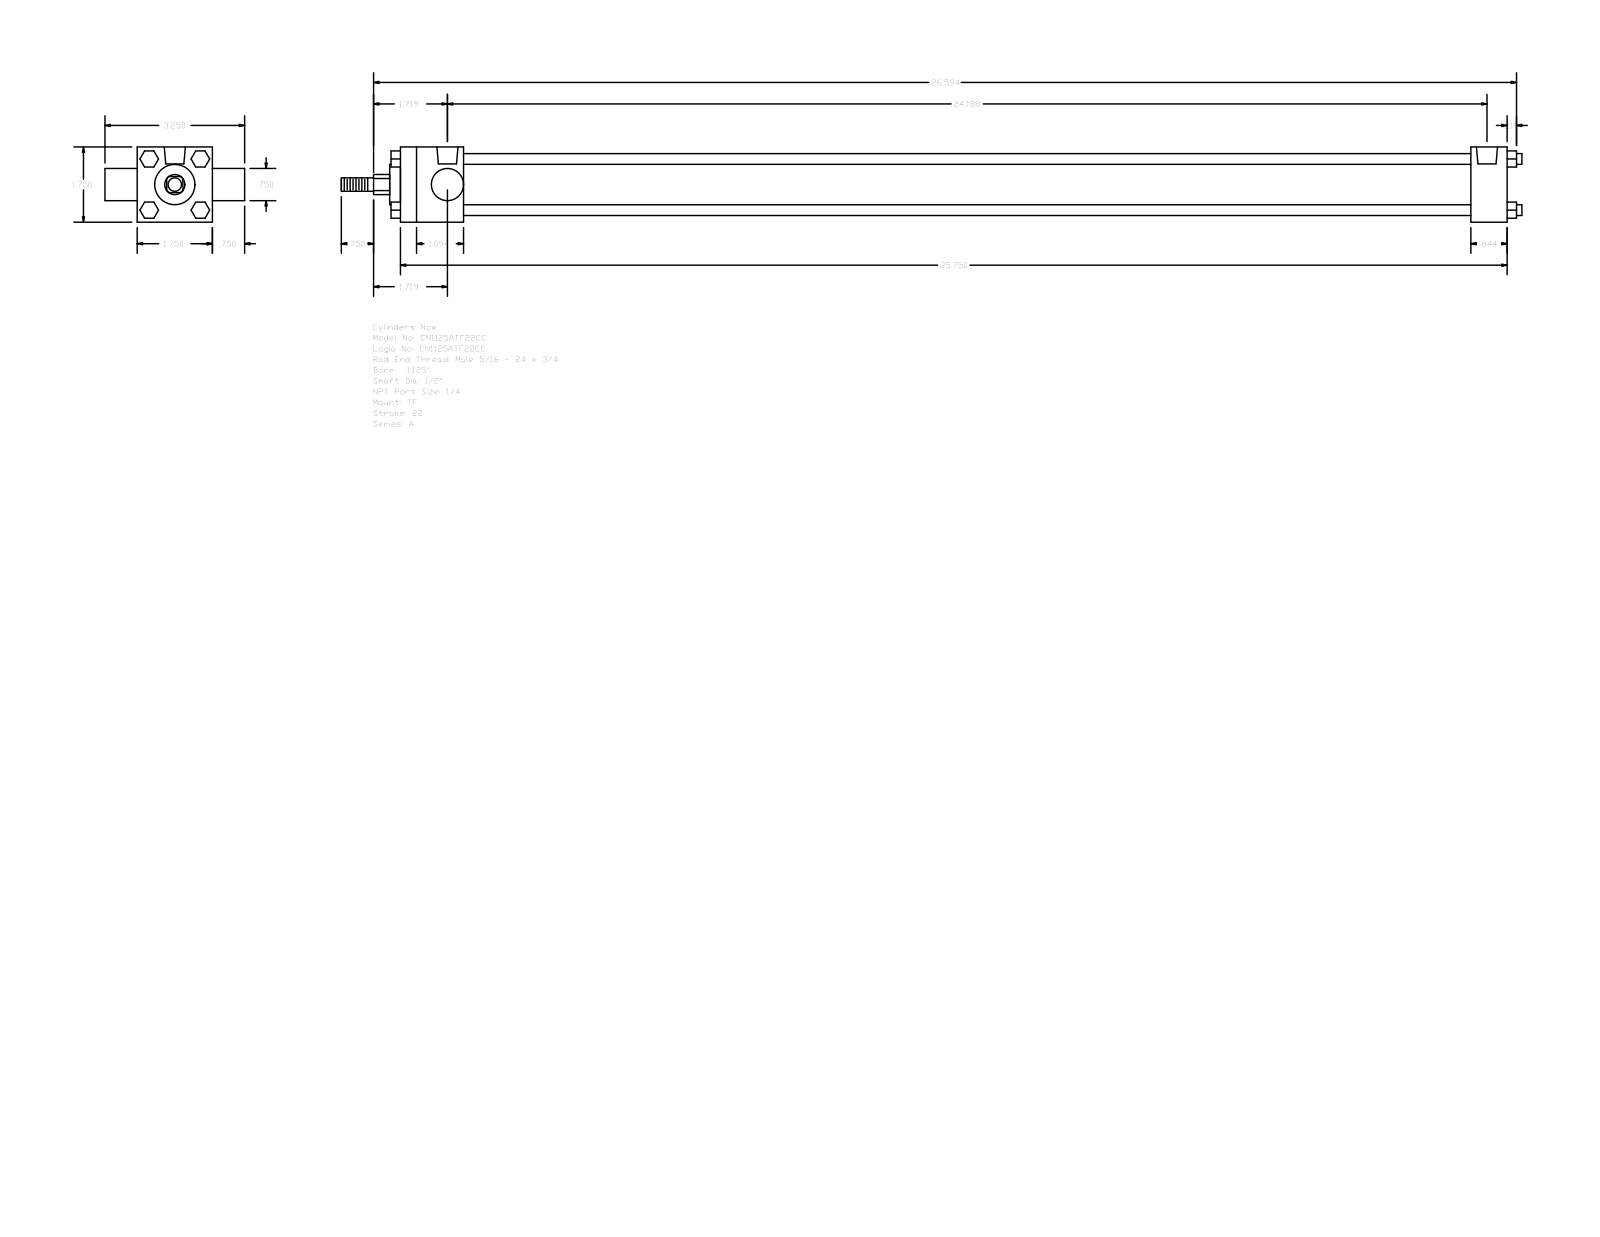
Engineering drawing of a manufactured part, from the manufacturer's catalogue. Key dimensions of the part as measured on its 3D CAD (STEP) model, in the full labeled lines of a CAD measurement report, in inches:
Part name (STEP PRODUCT): A_TF__0112_0.5
STEP written by: GSSL Pune (CONFIG_CONTROL_DESIGN)
Units: inches
Bodies: 0 solids, 120 faces (92 planar, 28 cylindrical, 0 other)
Overall size (bounding box): 27.469 × 3.25 × 1.75
Round holes (diameter × count): ⌀0.219 ×3, ⌀0.492 ×2
Round bosses / shafts (diameter × count): ⌀0.25 ×4, ⌀1.255 ×1, ⌀0.937 ×1, ⌀0.75 ×1, ⌀0.5 ×1, ⌀0.313 ×1
Partial cylindrical surfaces — rounded edges, fillets, slot ends (radius × count): R0.234 ×1
Main face-to-face distances: 1.75, 25.75, 24.906, 0.844, 1.469, 23.437, 24.281, 0.75, 2.5, 0.375
Hole centre spacings: 0.062, 0.063, 24.063, 24.125, 24.125, 24.187
